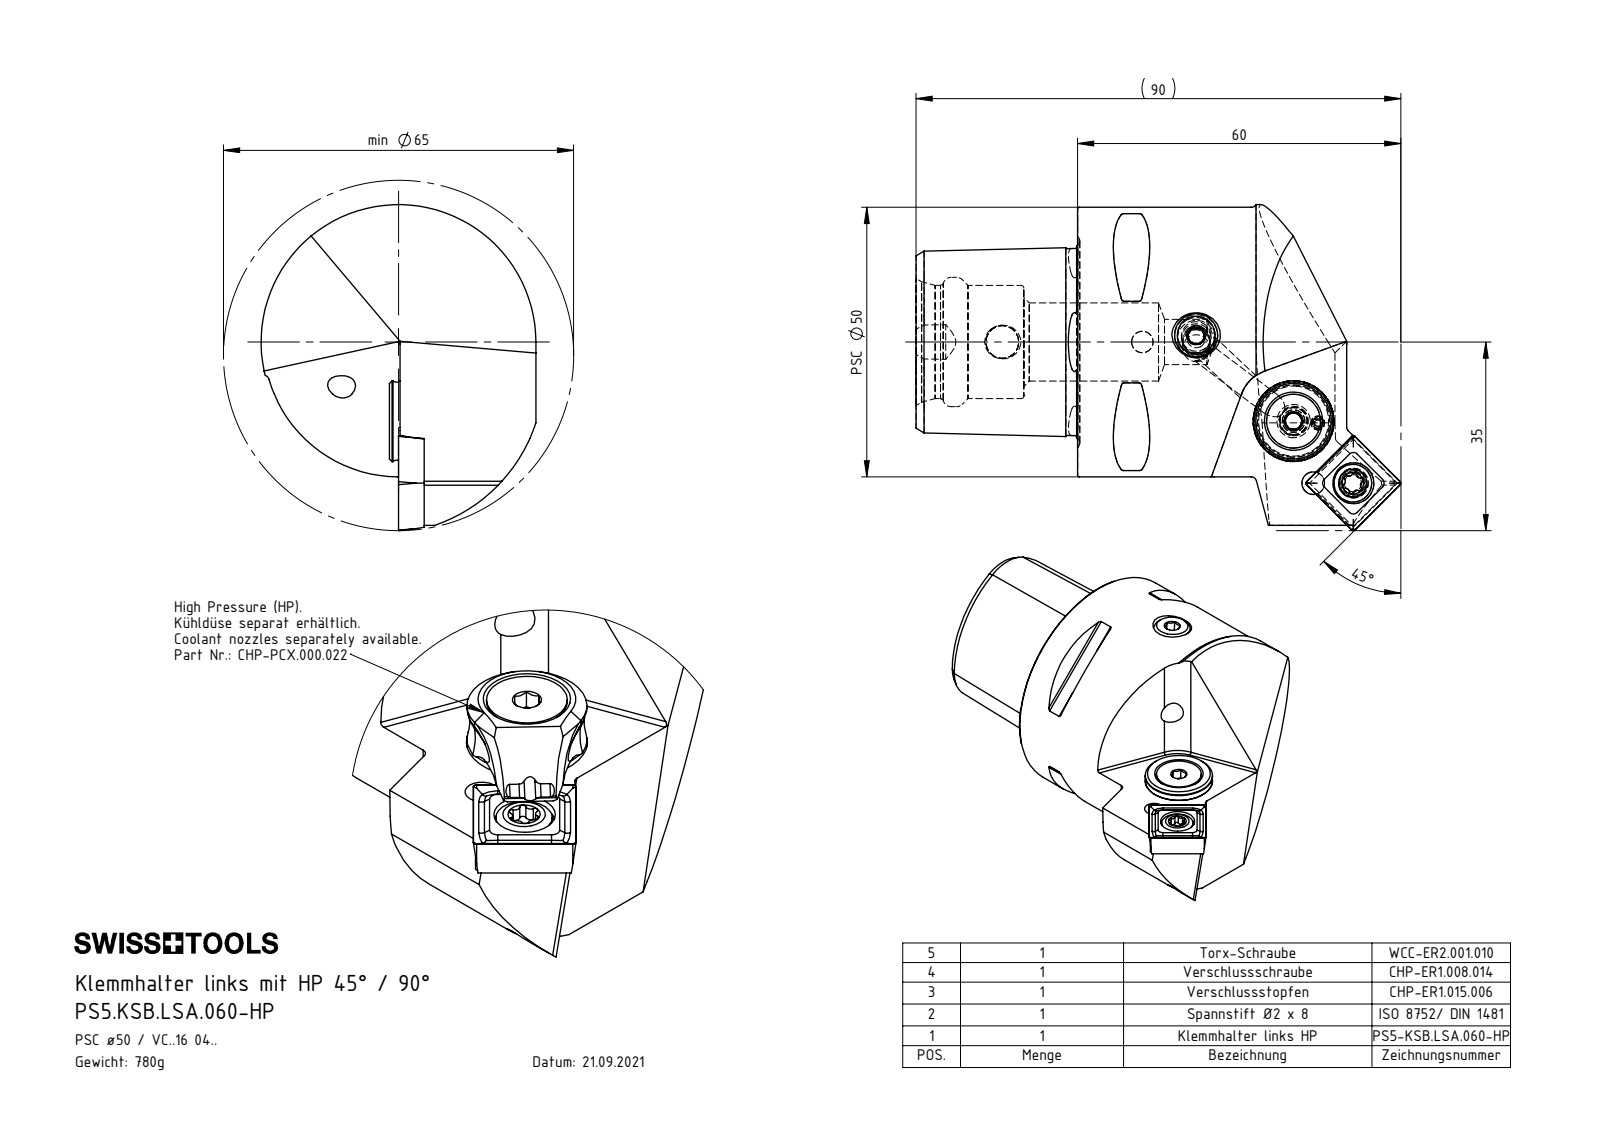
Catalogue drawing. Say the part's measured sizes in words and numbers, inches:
The part is named "PS5.KSB.LSA.060-HP; CHP-ER1.008.014_A; DIN 3771 - 13x1; PS5-KSB.LSA.060-HP_A (+7 more)". Its 3-D file was written by "SolidWorks 2022 (CONFIG_CONTROL_DESIGN)". It is 9 solids with 479 faces: 102 planar, 136 cylindrical and 241 other. Overall it measures 3.543 by 2.382 by 2.008 inches. Its volume is 6.049 cubic inches and its surface area 35.6 square inches. Round holes: 4 of diameter 0.165, 2 of diameter 0.197, 1 of diameter 0.047, 1 of diameter 0.079, 1 of diameter 0.118, 1 of diameter 0.157, 1 of diameter 0.209, 1 of diameter 0.217, 1 of diameter 0.24, 1 of diameter 0.276, 1 of diameter 0.299, 1 of diameter 0.331. Round bosses or shafts: 2 of diameter 0.197, 1 of diameter 1.969, 1 of diameter 0.585, 1 of diameter 0.528, 1 of diameter 0.394, 1 of diameter 0.315, 1 of diameter 0.276, 1 of diameter 0.217. Partial cylindrical surfaces (rounded edges, fillets, slot ends): 12 of radius 0.02, 7 of radius 0.039, 6 of radius 0.015, 6 of radius 0.027, 3 of radius 0.236, 2 of radius 0.043, 2 of radius 0.047, 2 of radius 0.197. The main face-to-face distances are 1.181, 0.176, 0.817, 0.992, 0.755, 0.815, 0.177, 1.748, 0.059, 0.118. The hole center spacings are 0.177, 0.29, 0.294, 0.441, 0.476, 0.509, 0.511, 0.627.
